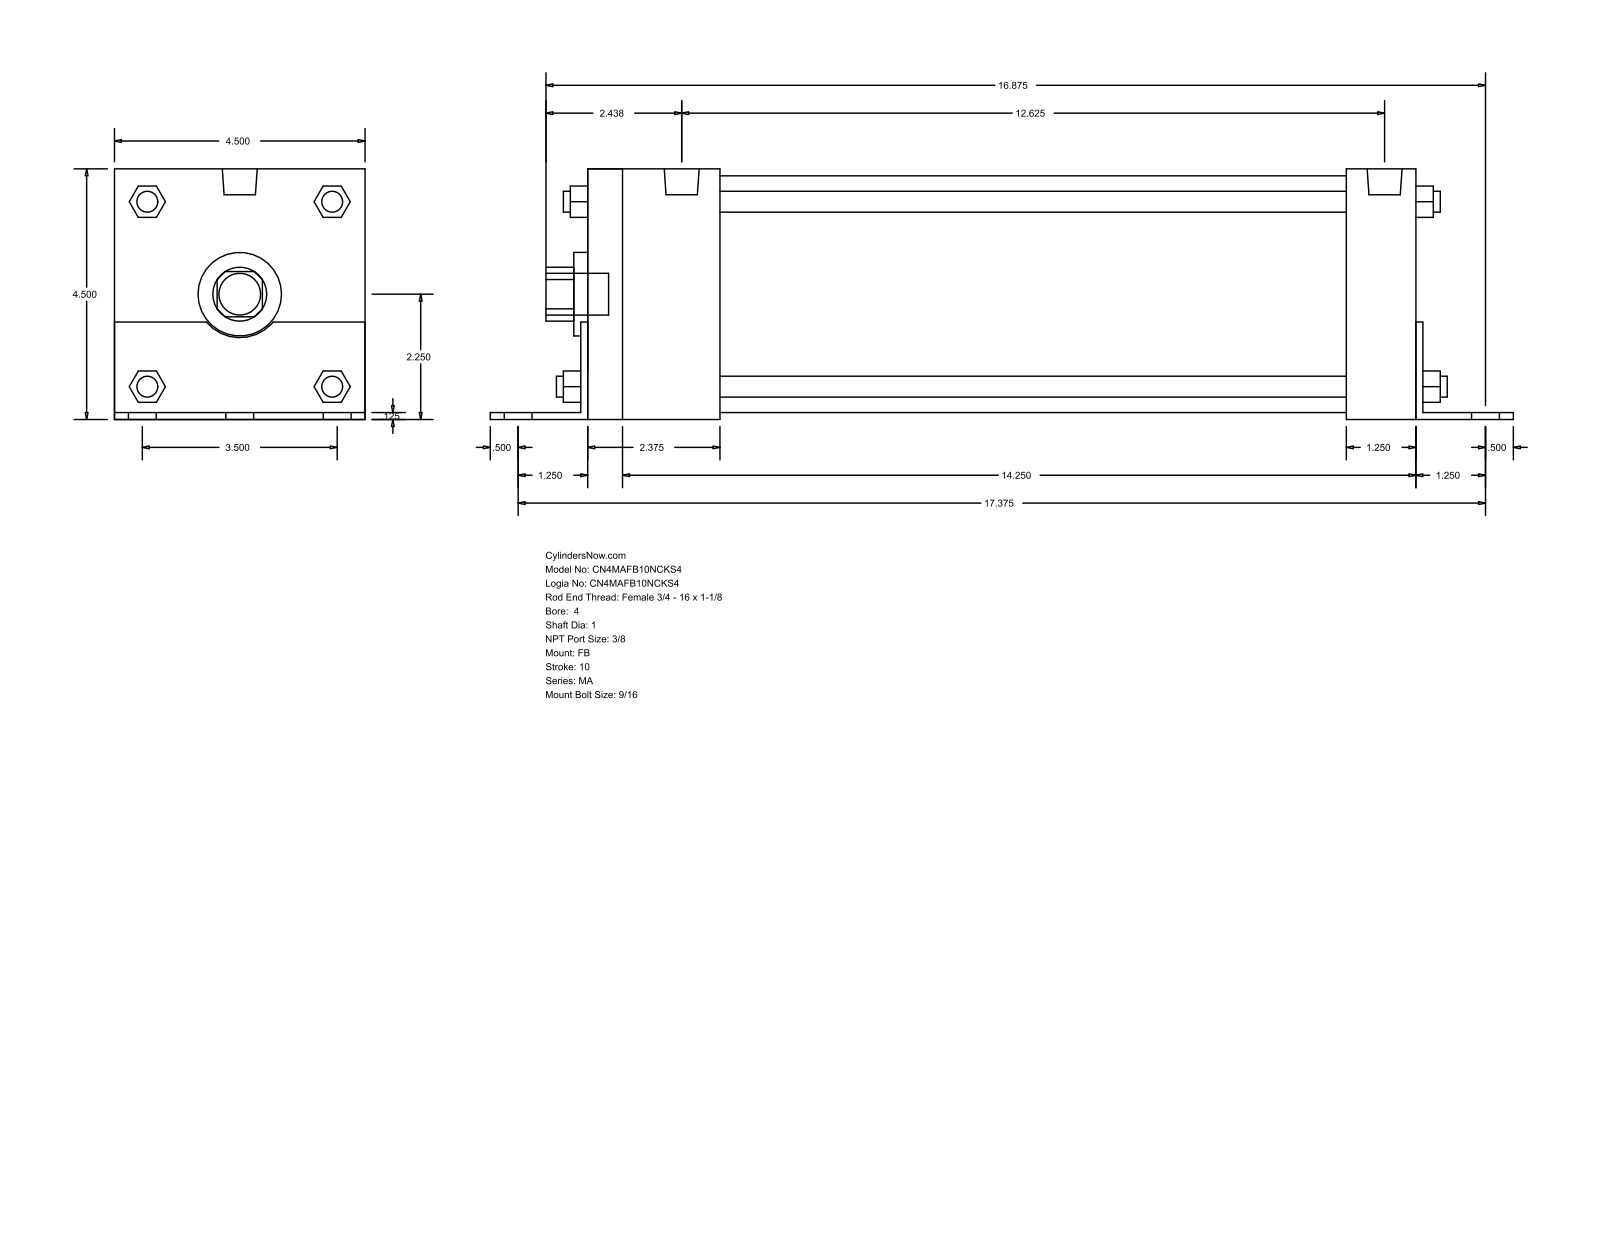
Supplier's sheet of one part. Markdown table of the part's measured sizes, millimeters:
| quantity | value |
| --- | --- |
| part name | MA_FB__0400_1 |
| STEP written by | GSSL Pune (CONFIG_CONTROL_DESIGN) |
| units | millimeters |
| bodies | 0 solids, 140 faces (105 planar, 35 cylindrical, 0 other) |
| overall size | 466.73 × 114.35 × 114.3 |
| round holes (diameter × count) | 25.4 × 1, 38.1 × 1, 107.95 × 1 |
| round bosses / shafts (diameter × count) | 14.29 × 6, 11.11 × 4, 9.53 × 4, 15.93 × 2, 19.05 × 1 |
| partial cylindrical surfaces (radius × count) | 12.29 × 1, 19.81 × 1 |
| main face-to-face distances | 114.3, 3.17, 114.35, 381, 3.12, 111.18, 377.83, 384.17, 34.93, 349.24 |
